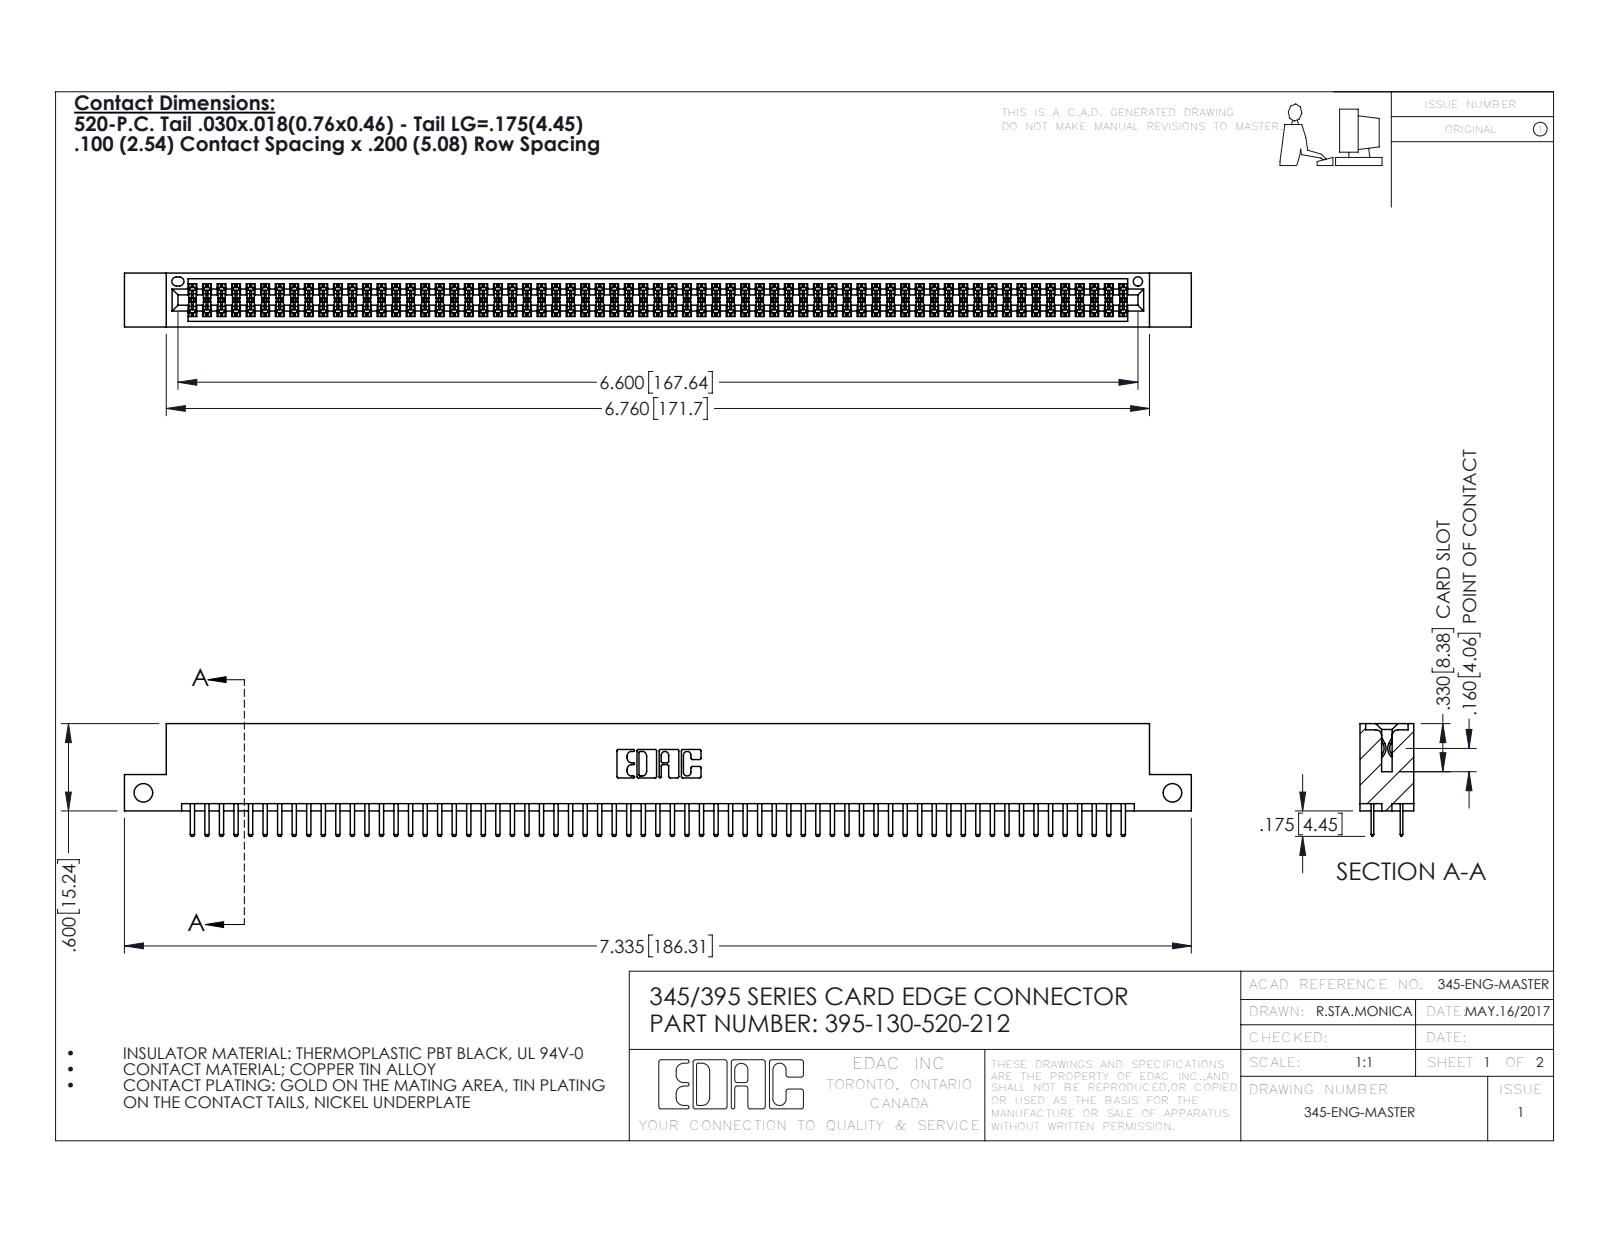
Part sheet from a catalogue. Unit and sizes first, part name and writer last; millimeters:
Units: millimetres
Overall size (bounding box): 186.3 × 19.7 × 9.4
Round holes (diameter × count): ⌀3.3 ×2, ⌀1.6 ×1
Partial cylindrical surfaces — rounded edges, fillets, slot ends (radius × count): R0.2 ×195, R0.3 ×134, R0.3 ×22, R0.2 ×6, R0.8 ×6, R0.7 ×3, R0.4 ×2, R0.5 ×2
Main face-to-face distances: 7.6, 1.8, 5.1, 9.4, 2.5, 6.9, 0.6, 5.7, 0.6, 1.8
Hole centre spacings: 179.7
Volume: 18 170 mm³ · Surface area: 27 050 mm²
Bodies: 131 solids, 7146 faces (4630 planar, 2516 cylindrical, 0 other)
Part name (STEP PRODUCT): 395-130-520-212; 345-292-001_345-293-120; 345 Part_Flush Mounting Lugs - Side Mount
STEP written by: SolidWorks 2016 (CONFIG_CONTROL_DESIGN)
